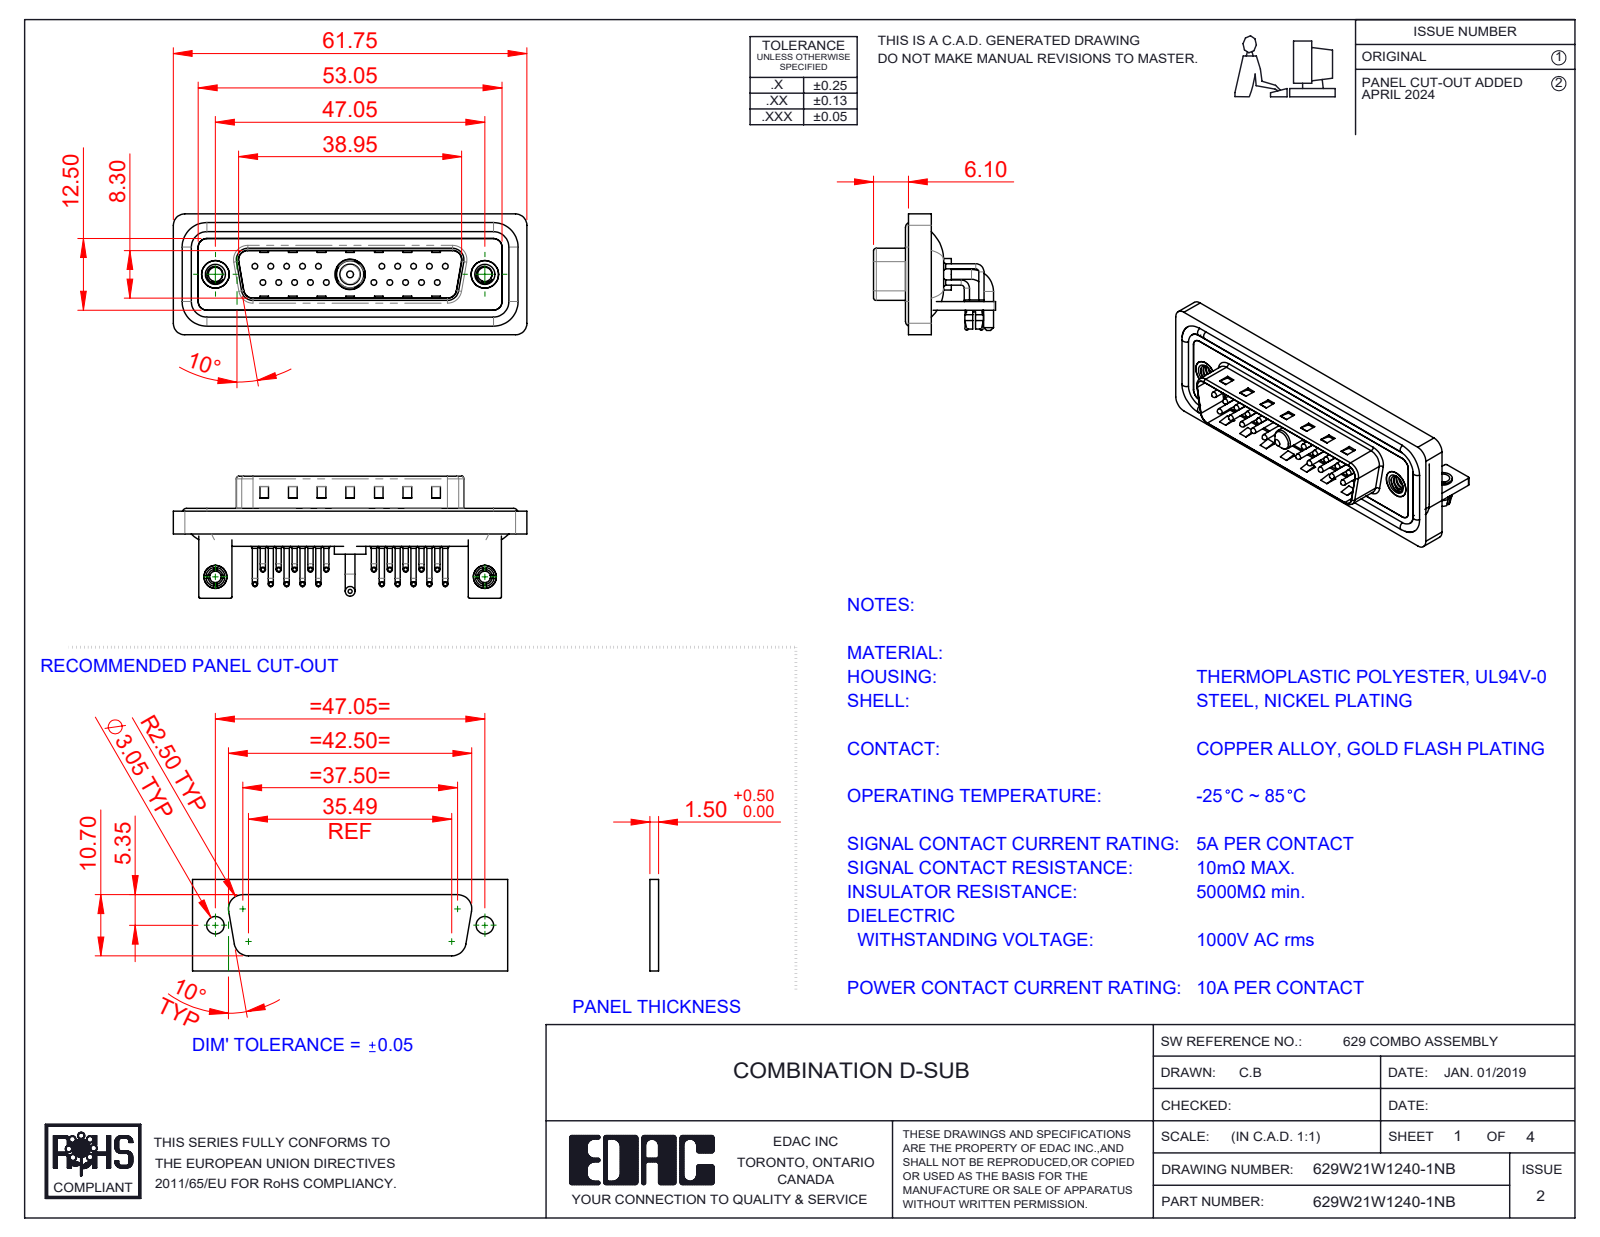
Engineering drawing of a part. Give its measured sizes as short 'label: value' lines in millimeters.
name: 629Combo Threaded Rivet_B; 629Combo Contact Row 2; 629Combo Stabilizer Bracket; 629Combo Shell Front_25 Contacts (+7 more)
written by: SolidWorks 2023 (CONFIG_CONTROL_DESIGN)
unit: mm
bodies: 33 solids, 2856 faces (1567 planar, 979 cylindrical, 310 other)
size: 61.75 × 21.3 × 21.1
volume: 7 668 mm³; area: 13 468 mm²
holes: 22× ⌀2, 20× ⌀0.75, 20× ⌀1.6, 4× ⌀2.5, 2× ⌀3.2, 2× ⌀4, 2× ⌀4.8, 2× ⌀5, 1× ⌀4.85, 1× ⌀5.3
bosses: 40× ⌀0.9, 20× ⌀1.5, 20× ⌀1, 20× ⌀0.65, 4× ⌀1.6, 2× ⌀4.9, 2× ⌀4, 2× ⌀3.4
rounds: 20× R1.01, 19× R2, 18× R1.5, 16× R0.25, 9× R0.5, 8× R1.6, 4× R0.6, 4× R0.65
face distances: 0.4, 0.8, 2.1, 2.9, 1.5, 1.1, 4.1, 1.6, 4.5, 3.7
hole spacings: 3.16, 2.77, 5.54, 8.31, 5.04, 19.39, 20.97, 22.16
